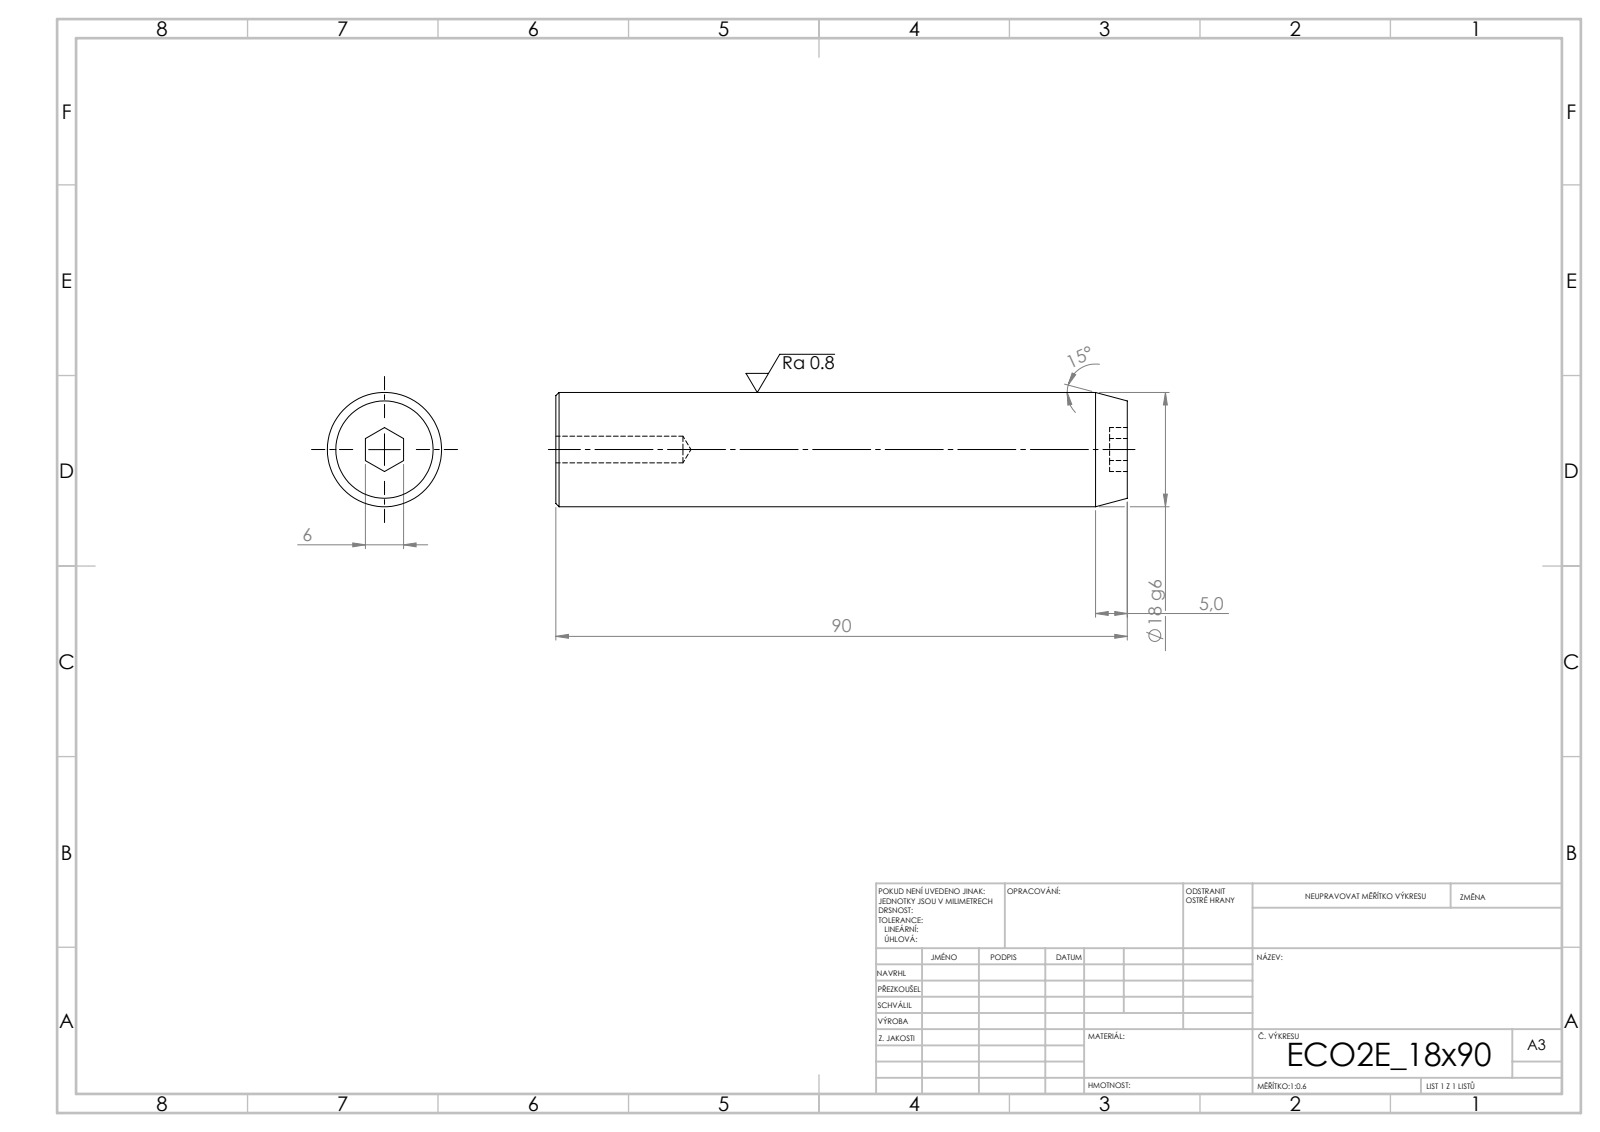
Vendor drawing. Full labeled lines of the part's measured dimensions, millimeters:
STEP written by: SolidWorks 2019 (CONFIG_CONTROL_DESIGN)
Units: millimetres
Bodies: 1 solid, 19 faces (9 planar, 4 cylindrical, 6 other)
Overall size (bounding box): 90 × 18 × 18
Volume: 22 345 mm³ · Surface area: 5 824 mm²
Round holes (diameter × count): ⌀4.2 ×1
Round bosses / shafts (diameter × count): ⌀18 ×1
Main face-to-face distances: 90, 2.8, 87.2, 6
